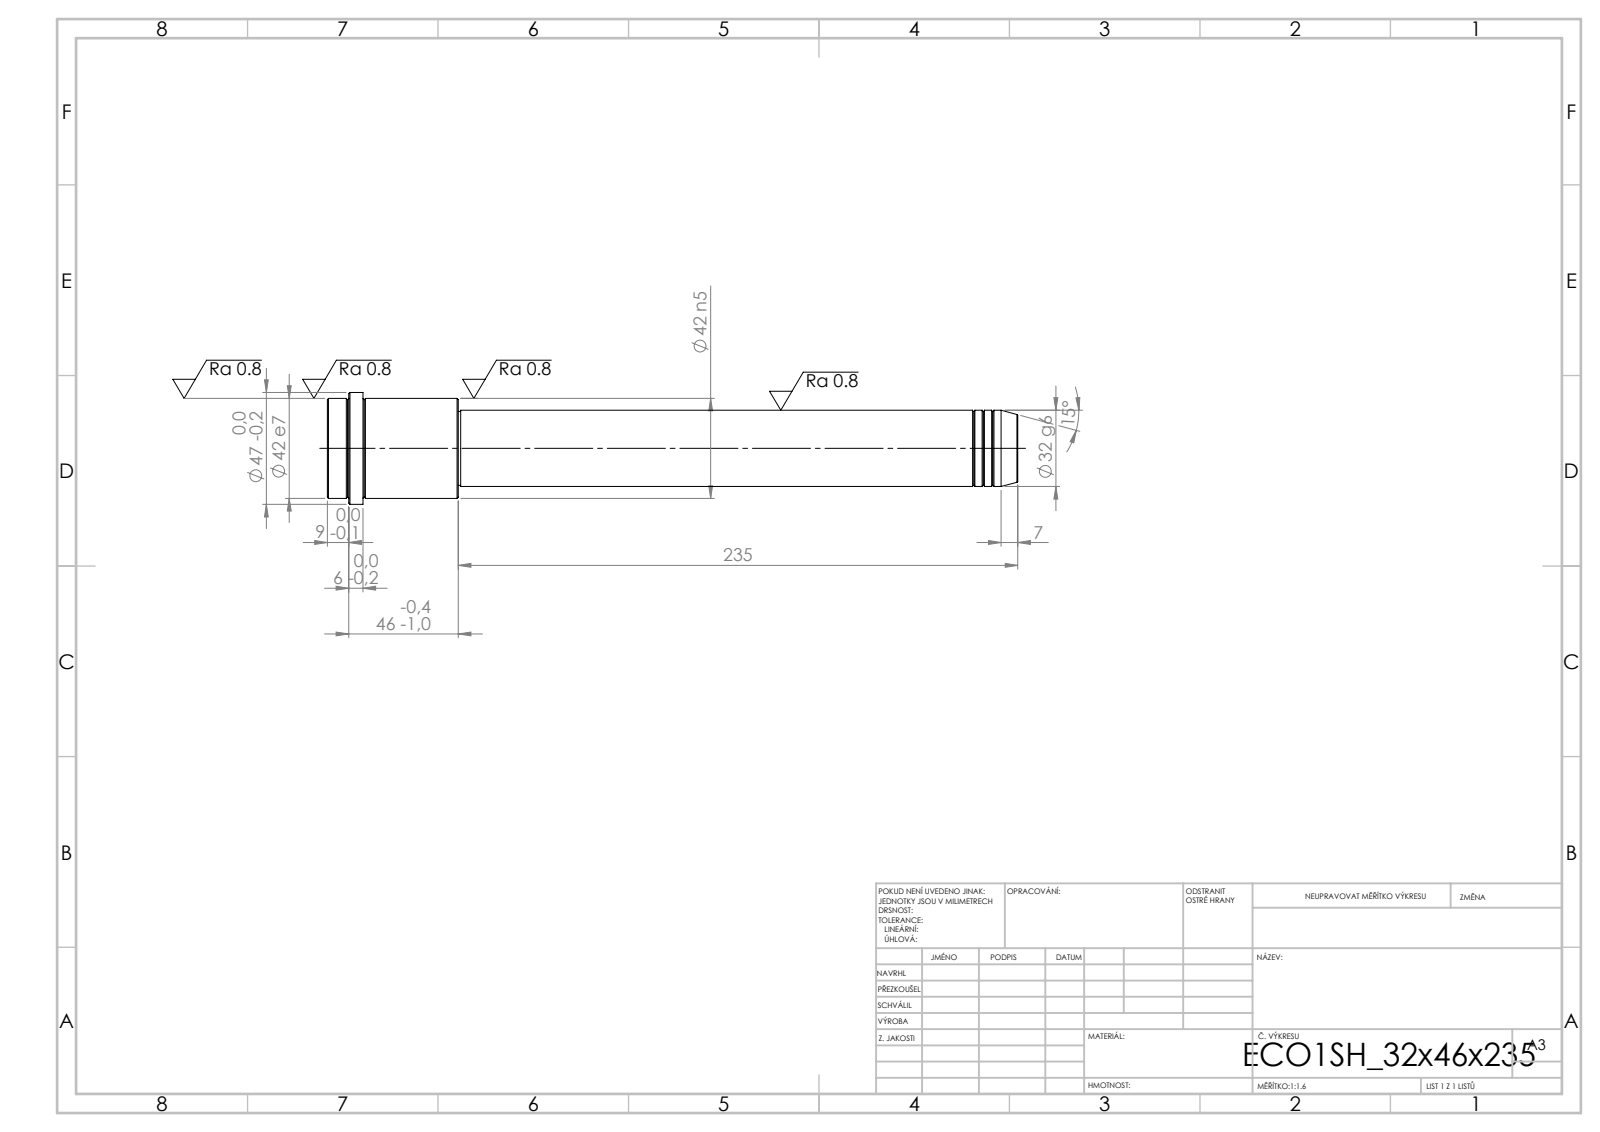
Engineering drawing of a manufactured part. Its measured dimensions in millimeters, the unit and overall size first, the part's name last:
Units: millimetres
Overall size (bounding box): 290 × 47 × 47
Round bosses / shafts (diameter × count): ⌀47 ×1, ⌀42 ×1, ⌀32 ×1, ⌀31 ×1
Main face-to-face distances: 290, 235, 55, 275, 40, 15, 281, 46, 6, 9
Volume: 266 338 mm³ · Surface area: 34 522 mm²
Bodies: 1 solid, 52 faces (6 planar, 16 cylindrical, 30 other)
STEP written by: SolidWorks 2019 (CONFIG_CONTROL_DESIGN)
